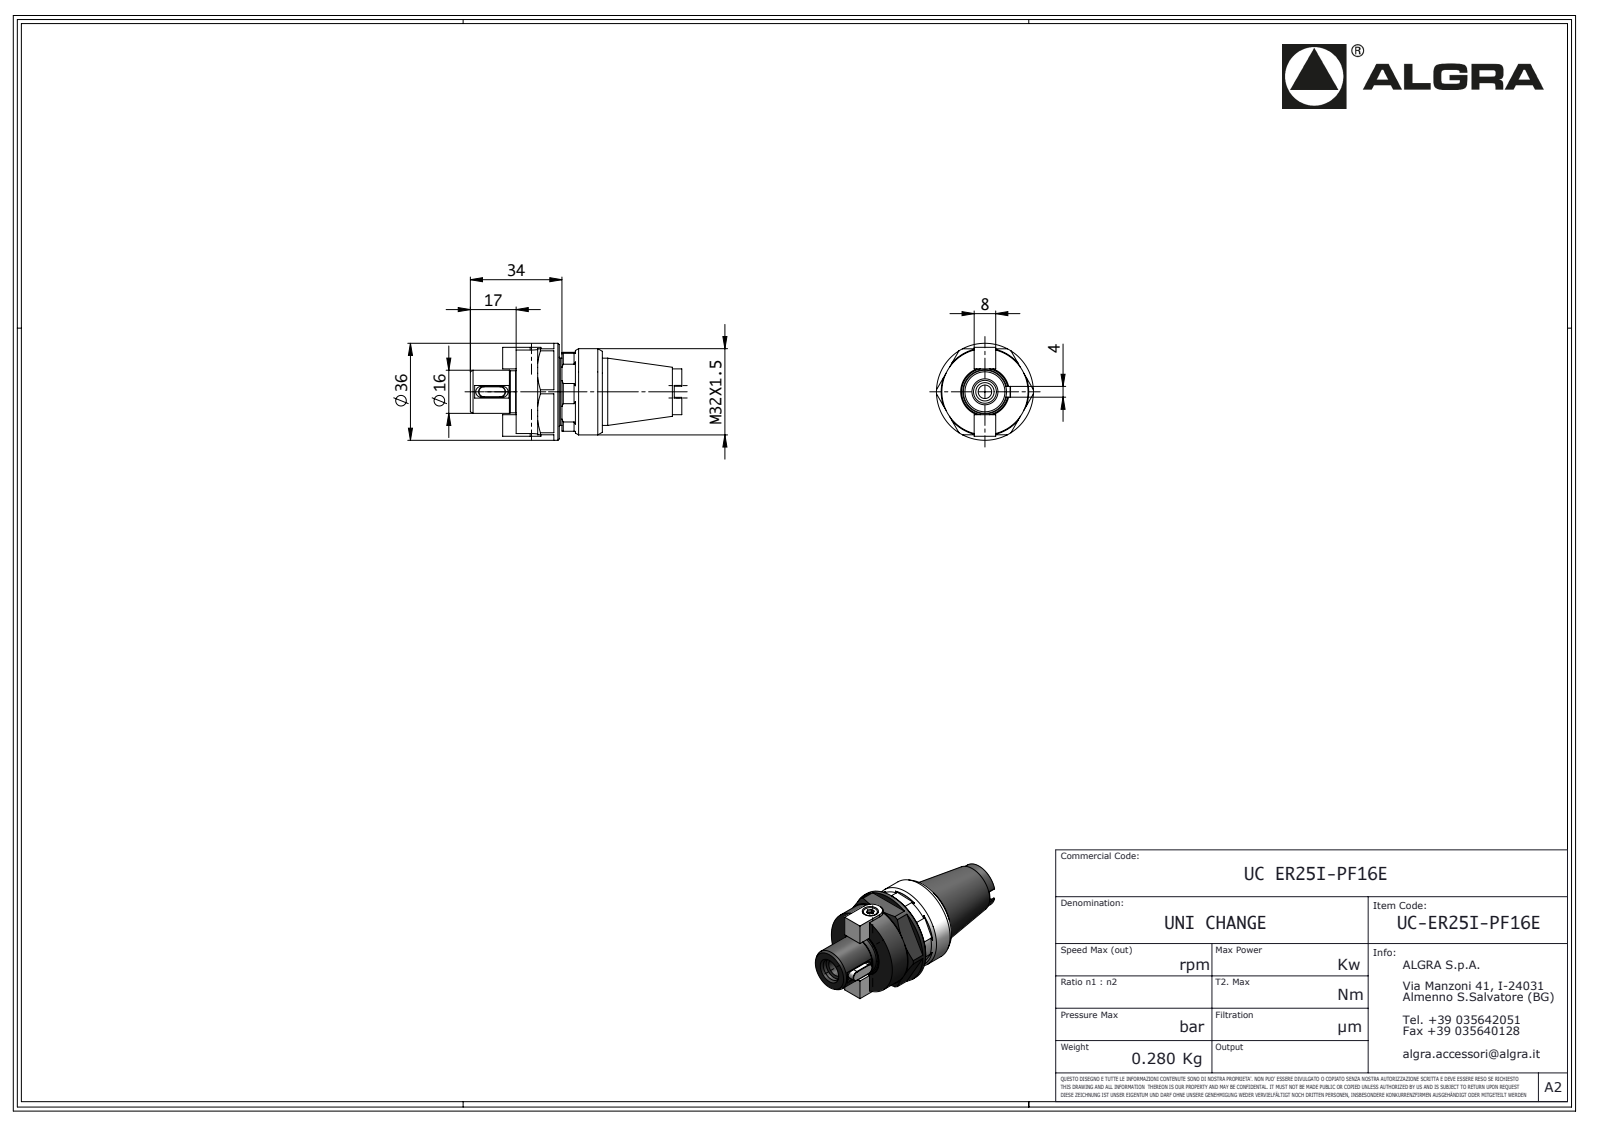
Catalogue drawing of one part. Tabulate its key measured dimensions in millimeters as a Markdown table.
| quantity | value |
| --- | --- |
| part name | UC-ER25I-PF16E |
| STEP written by | SolidWorks 2016 (AUTOMOTIVE_DESIGN) |
| units | millimeters |
| bodies | 0 solids, 195 faces (107 planar, 50 cylindrical, 38 other) |
| overall size | 84.5 × 36 × 36 |
| round holes (diameter × count) | 1.1 × 2, 1.5 × 2, 2.5 × 2, 5 × 1, 6 × 1, 25.05 × 1 |
| round bosses / shafts (diameter × count) | 36 × 1, 32 × 1, 24.95 × 1, 17 × 1, 16 × 1, 15.6 × 1, 5.5 × 1 |
| partial cylindrical surfaces (radius × count) | 0.24 × 4, 2 × 4, 0.16 × 2, 3.81 × 2, 4 × 2, 5.05 × 1, 10 × 1, 15.03 × 1 |
| main face-to-face distances | 16, 8, 17, 33, 6, 31.9, 18, 37, 39, 23 |
| hole center spacings | 5.25, 9.31, 13.65, 18.47, 10.5, 27.3 |
